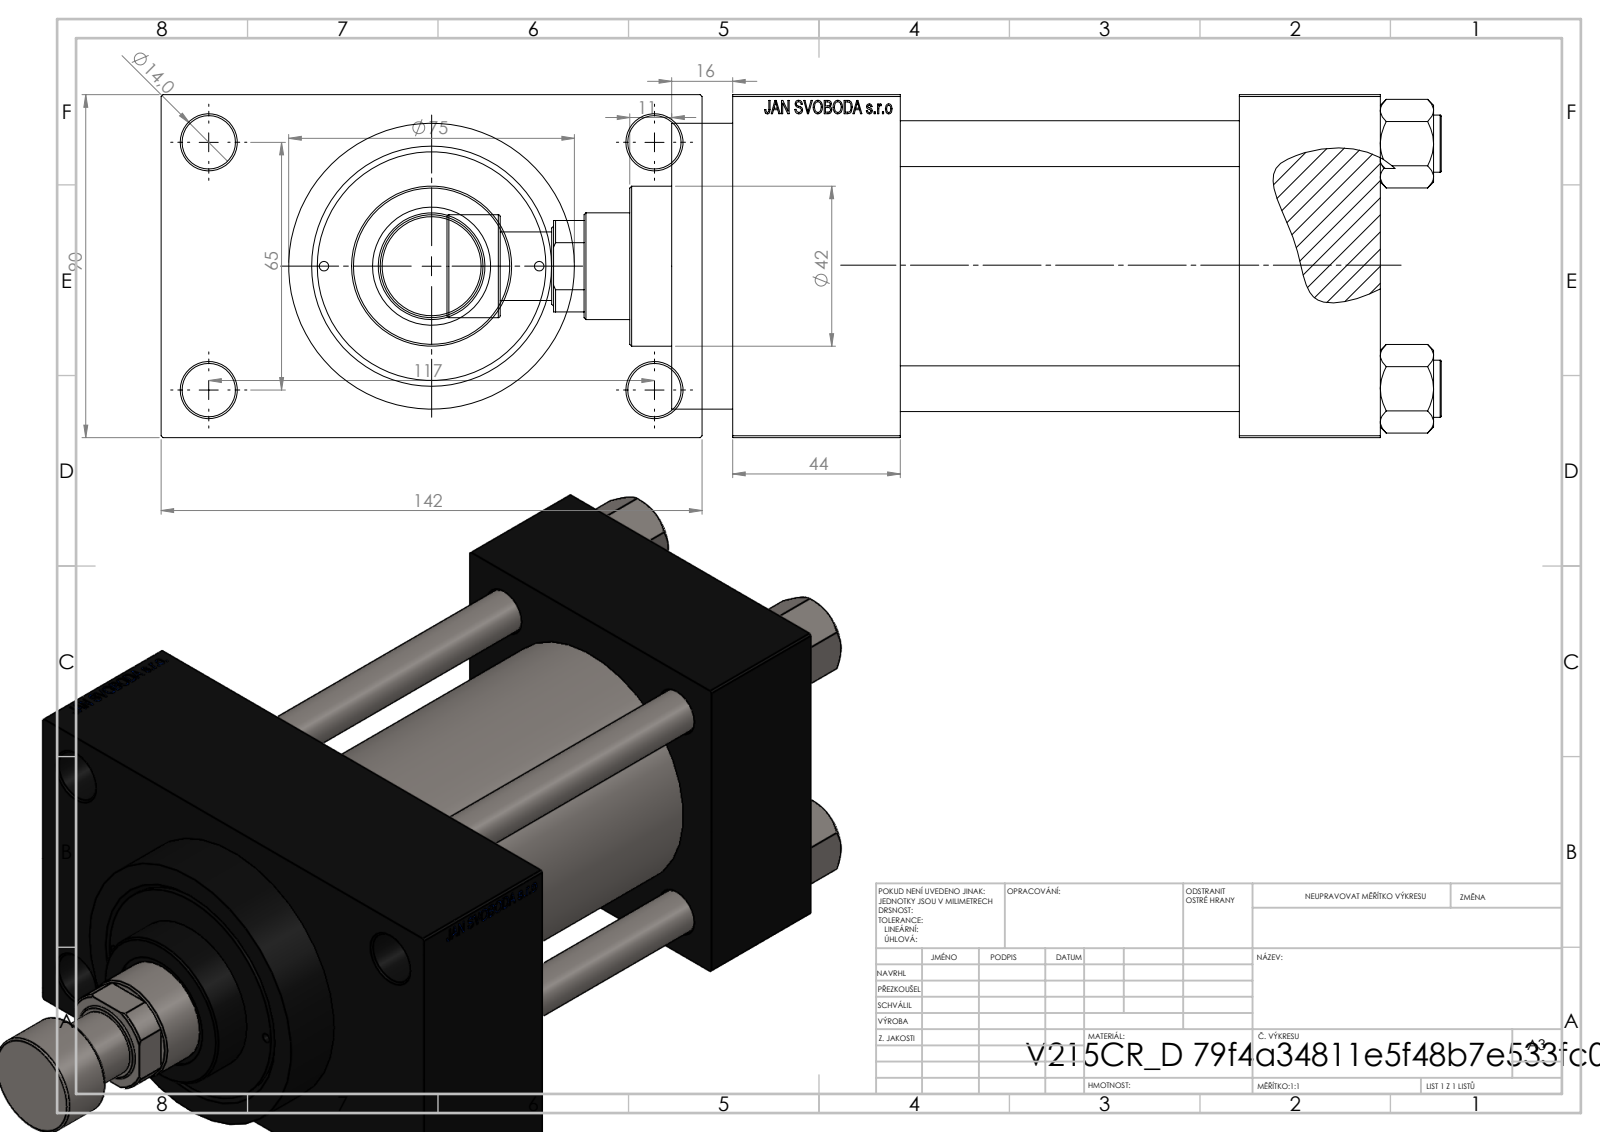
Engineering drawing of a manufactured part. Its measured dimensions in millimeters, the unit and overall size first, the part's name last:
Units: millimetres
Overall size (bounding box): 261 × 142 × 90
Round holes (diameter × count): ⌀12 ×4, ⌀14 ×4, ⌀2.5 ×2, ⌀7 ×2, ⌀20.96 ×2, ⌀30 ×2, ⌀18.5 ×1, ⌀28 ×1, ⌀31 ×1, ⌀50 ×1, ⌀60 ×1, ⌀63 ×1
Round bosses / shafts (diameter × count): ⌀15 ×4, ⌀75 ×1, ⌀69 ×1, ⌀42 ×1, ⌀27 ×1, ⌀18 ×1
Main face-to-face distances: 90, 89, 37, 126, 133, 170, 44, 26, 116, 142
Hole centre spacings: 26.35, 32.39, 44.4, 45.47, 64.3, 66.92, 68.42, 69.81
Volume: 1 158 000 mm³ · Surface area: 223 090 mm²
Bodies: 12 solids, 1125 faces (503 planar, 96 cylindrical, 526 other)
Part name (STEP PRODUCT): V215CR_D_TYCINKA; NUT_M5_D; V215CR_D_Body; V215CR_VCP_D (+2 more)
STEP written by: SolidWorks 2019 (CONFIG_CONTROL_DESIGN)
